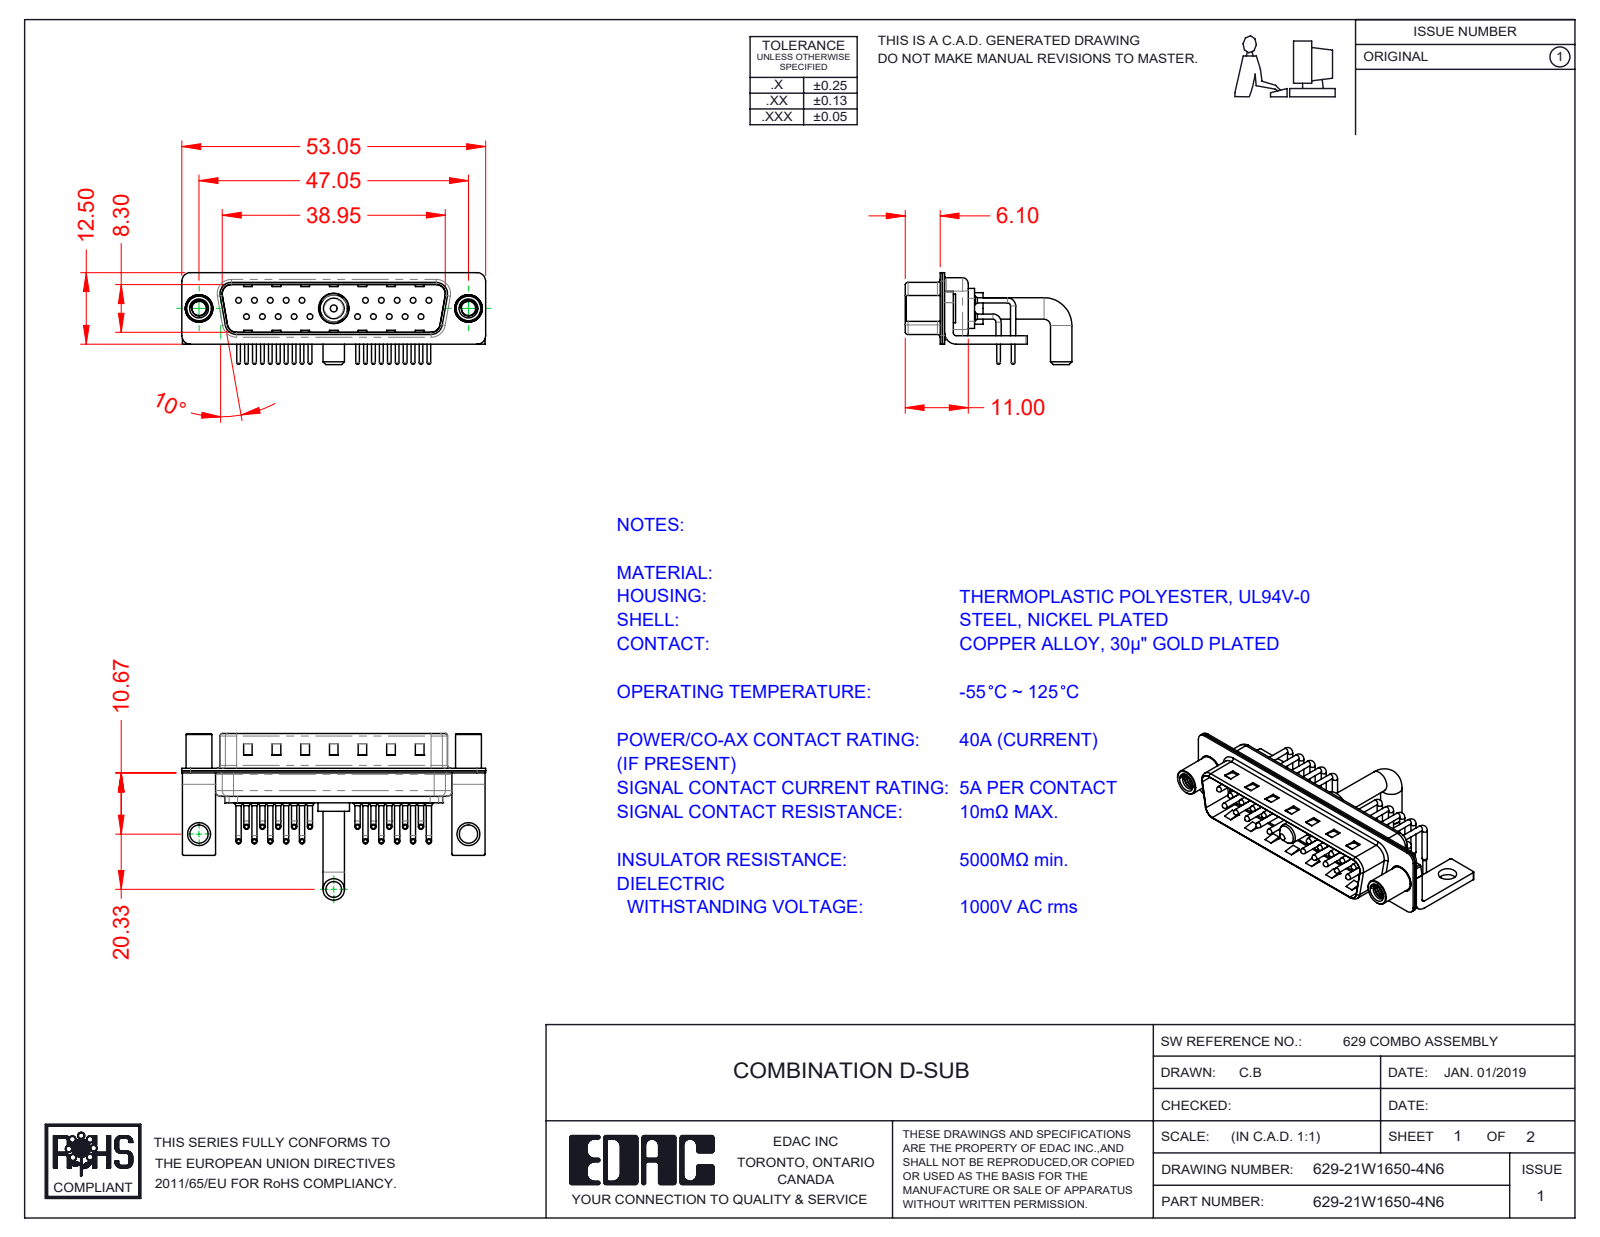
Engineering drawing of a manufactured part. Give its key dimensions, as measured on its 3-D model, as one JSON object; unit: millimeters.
{"part_name": "629Combo Shell Front_25 Contacts; 629Combo Shell Rear_25 Contacts; 629Combo Contact Row 1; 629Combo Threaded Standoff_D (+5 more)", "step_written_by": "SolidWorks 2020 (CONFIG_CONTROL_DESIGN)", "units": "millimeters", "bodies": {"solids": 29, "faces": 2717, "planar": 1483, "cylindrical": 950, "other": 284}, "overall_size": [53.05, 29.11, 16.05], "volume_mm3": 3553, "surface_area_mm2": 8648, "round_holes": [[0.75, 20], [1.6, 20], [2, 20], [2.5, 2], [3.2, 2], [4, 2], [4.8, 2], [4.85, 1], [5.3, 1]], "round_bosses_or_shafts": [[0.9, 40], [1.5, 20], [1, 20], [0.65, 20], [5, 2], [4.9, 2], [4.5, 2], [3.75, 2]], "partial_cylinders_radius": [[1.01, 20], [0.25, 16], [1.5, 16], [2, 13], [0.5, 9], [1.6, 8], [0.6, 4], [0.65, 4]], "face_to_face_distances": [0.4, 0.8, 9.5, 1.5, 9.1, 8.7, 9.9, 0.6, 2.1, 0.75], "hole_center_spacings": [3.16, 2.77, 5.54, 8.31, 5.04, 19.39, 20.97, 22.16]}
